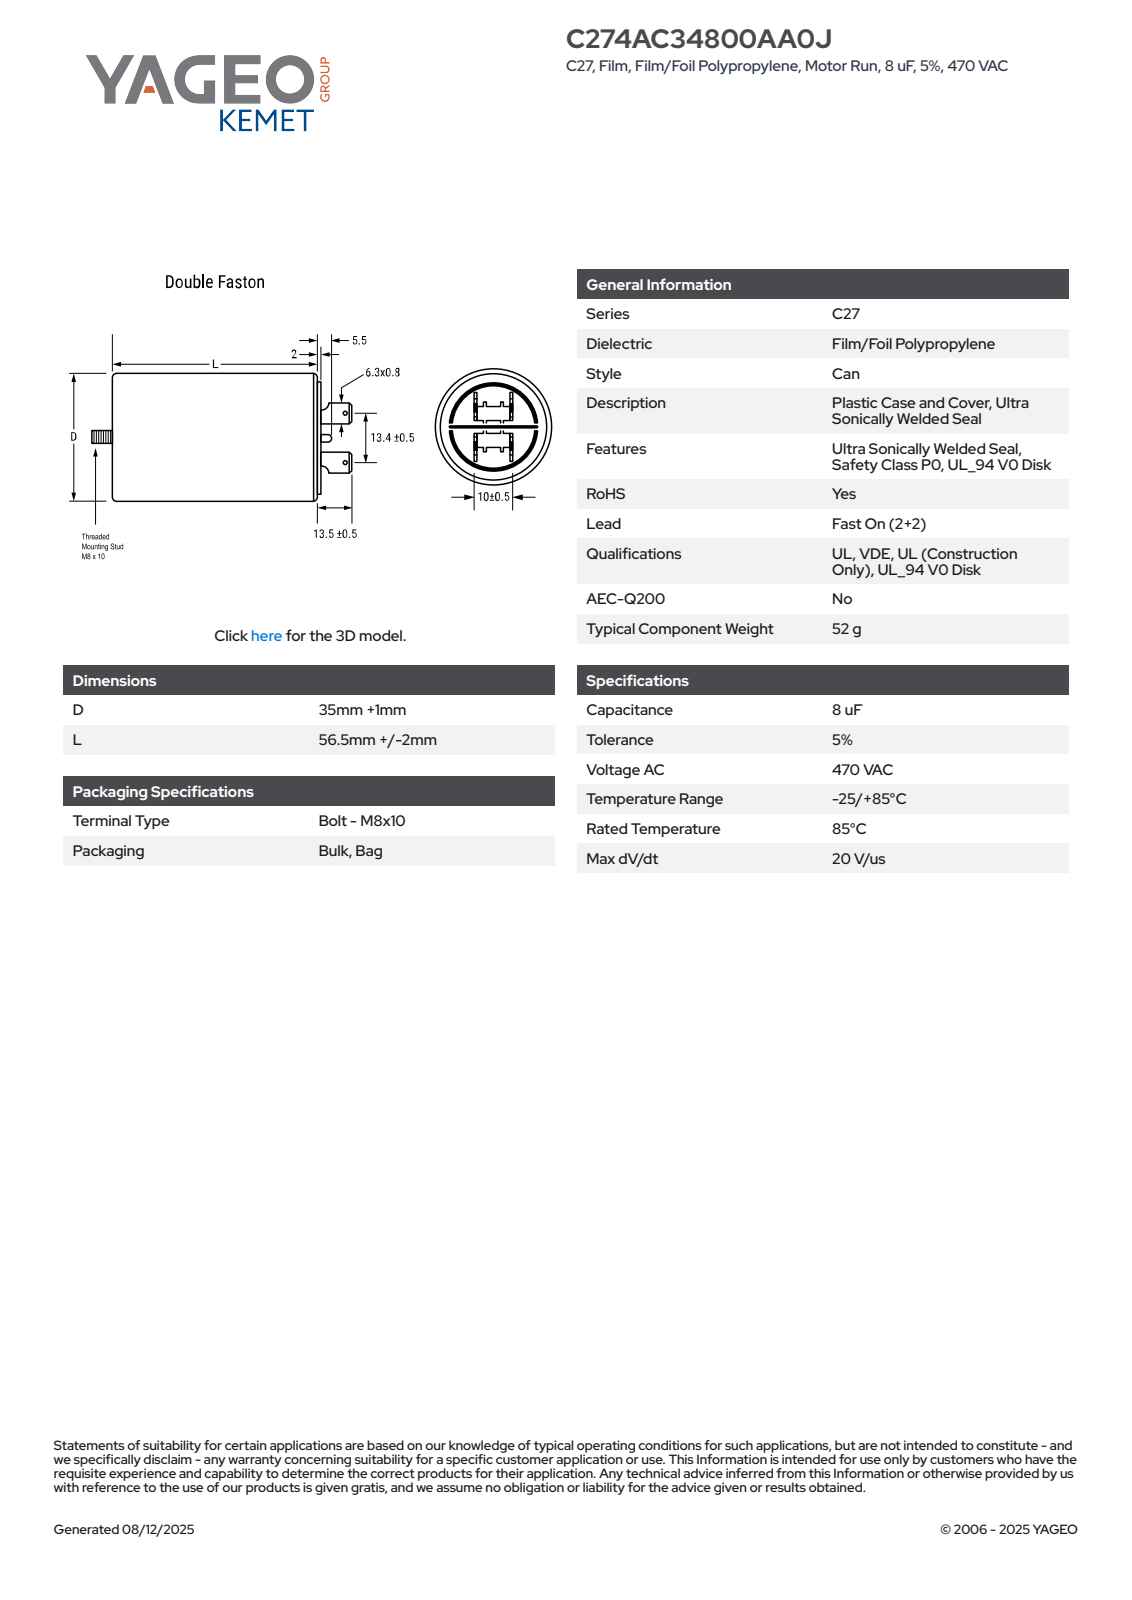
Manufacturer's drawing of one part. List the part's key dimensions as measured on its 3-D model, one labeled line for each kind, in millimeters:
Part name (STEP PRODUCT): CFM_C27DF_35X56.5_D36L58.5
STEP written by: SolidWorks 2014 (AUTOMOTIVE_DESIGN)
Units: millimetres
Bodies: 1 solid, 137 faces (49 planar, 53 cylindrical, 35 other)
Overall size (bounding box): 82.5 × 36 × 36
Volume: 61 335 mm³ · Surface area: 9 728 mm²
Round holes (diameter × count): ⌀1.2 ×2
Round bosses / shafts (diameter × count): ⌀36 ×1, ⌀27.69 ×1, ⌀8 ×1
Partial cylindrical surfaces — rounded edges, fillets, slot ends (radius × count): R0.25 ×9, R4 ×2, R17.99 ×1
Main face-to-face distances: 60.5, 0.8, 9.7, 58.5, 2, 10.5, 8.9, 0.5, 10, 68.5
Hole centre spacings: 13.9
